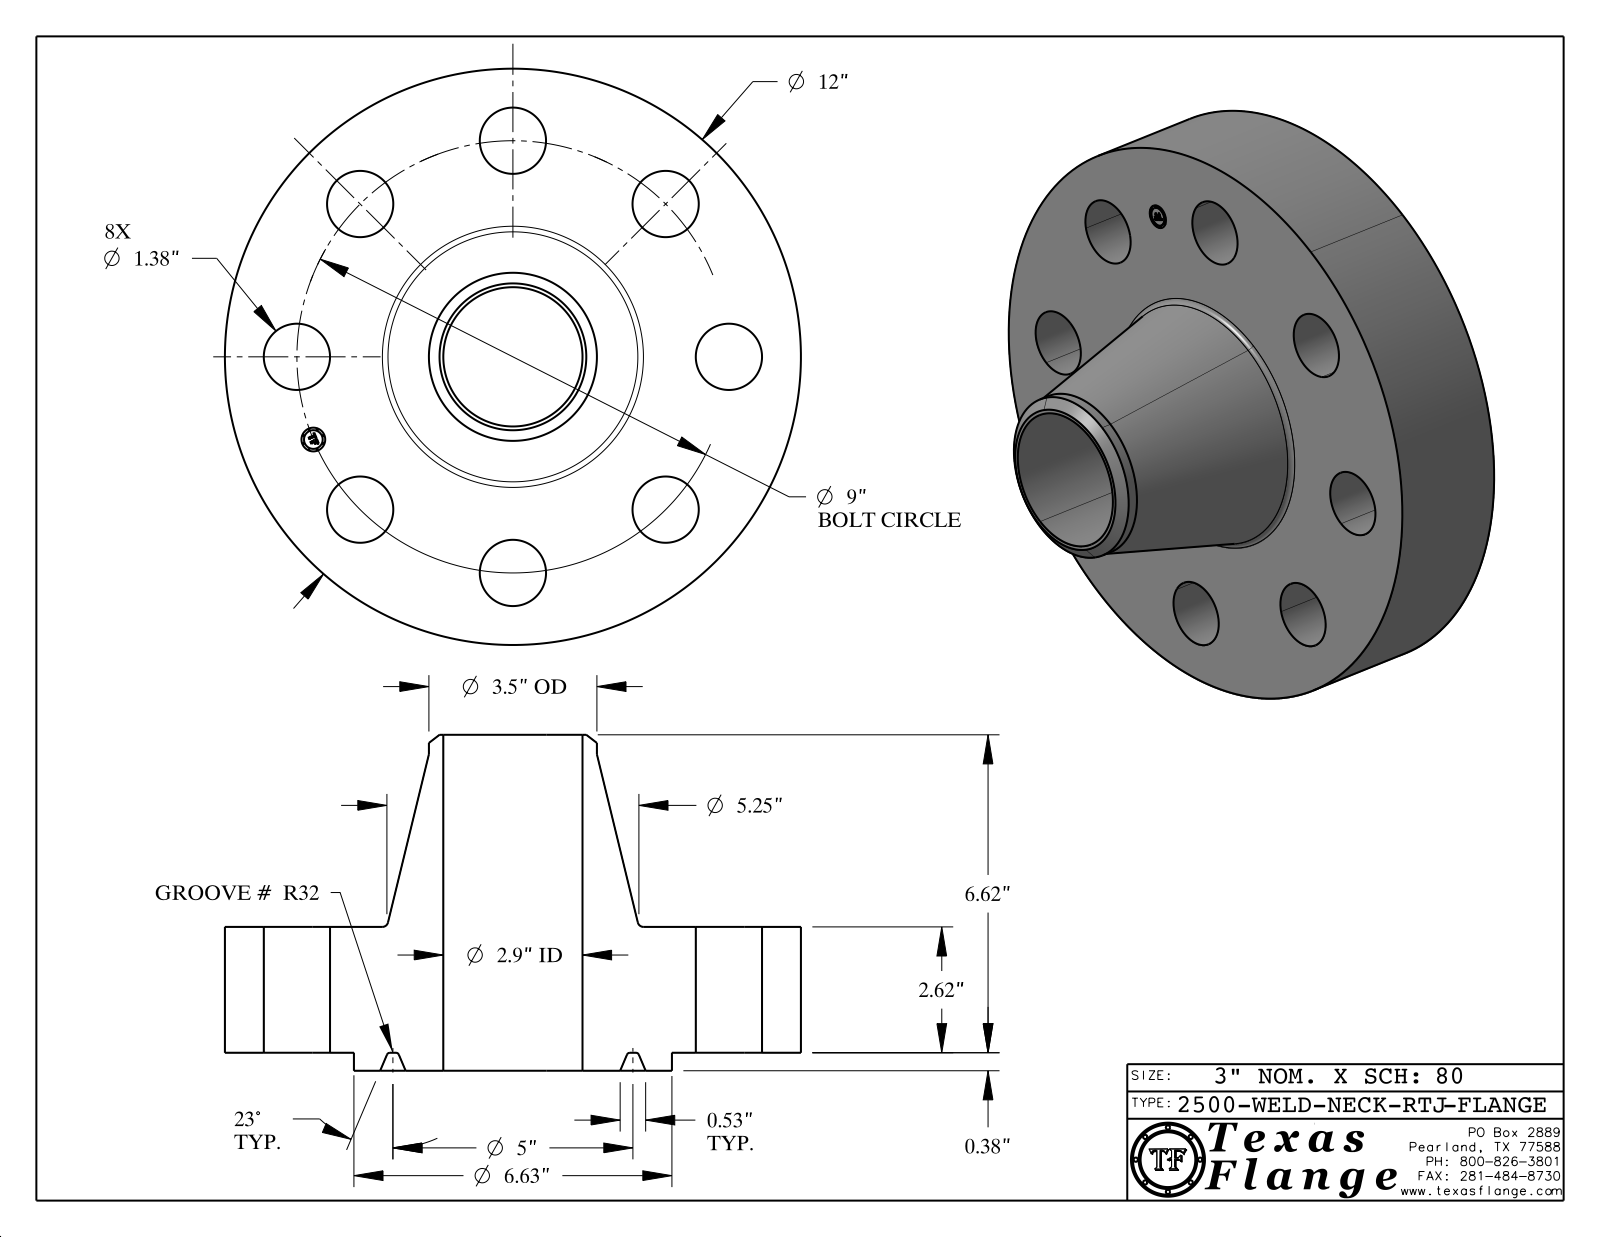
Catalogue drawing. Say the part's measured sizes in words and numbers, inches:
The part is named "2500-WELD-NECK-RTJ". Its 3-D file was written by "CATIA V5 STEP AP214 (AUTOMOTIVE_DESIGN)". It is 1 solid with 429 faces: 371 planar, 44 cylindrical and 14 other. Overall it measures 12 by 12 by 6.995 inches. Its volume is 288 cubic inches and its surface area 499.3 square inches. Round holes: 8 of diameter 1.38, 1 of diameter 0.495, 1 of diameter 2.9. Round bosses or shafts: 8 of diameter 0.03, 1 of diameter 12, 1 of diameter 6.625, 1 of diameter 3.5, 1 of diameter 0.39. The main face-to-face distances are 2.62, 0.375, 2.995, 6.995, 6.62, 4, 2.98, 2.605, 0.015, 4.015. The hole center spacings are 4.5, 3.444, 6.364, 8.315, 1.756, 5, 7.483, 9.
